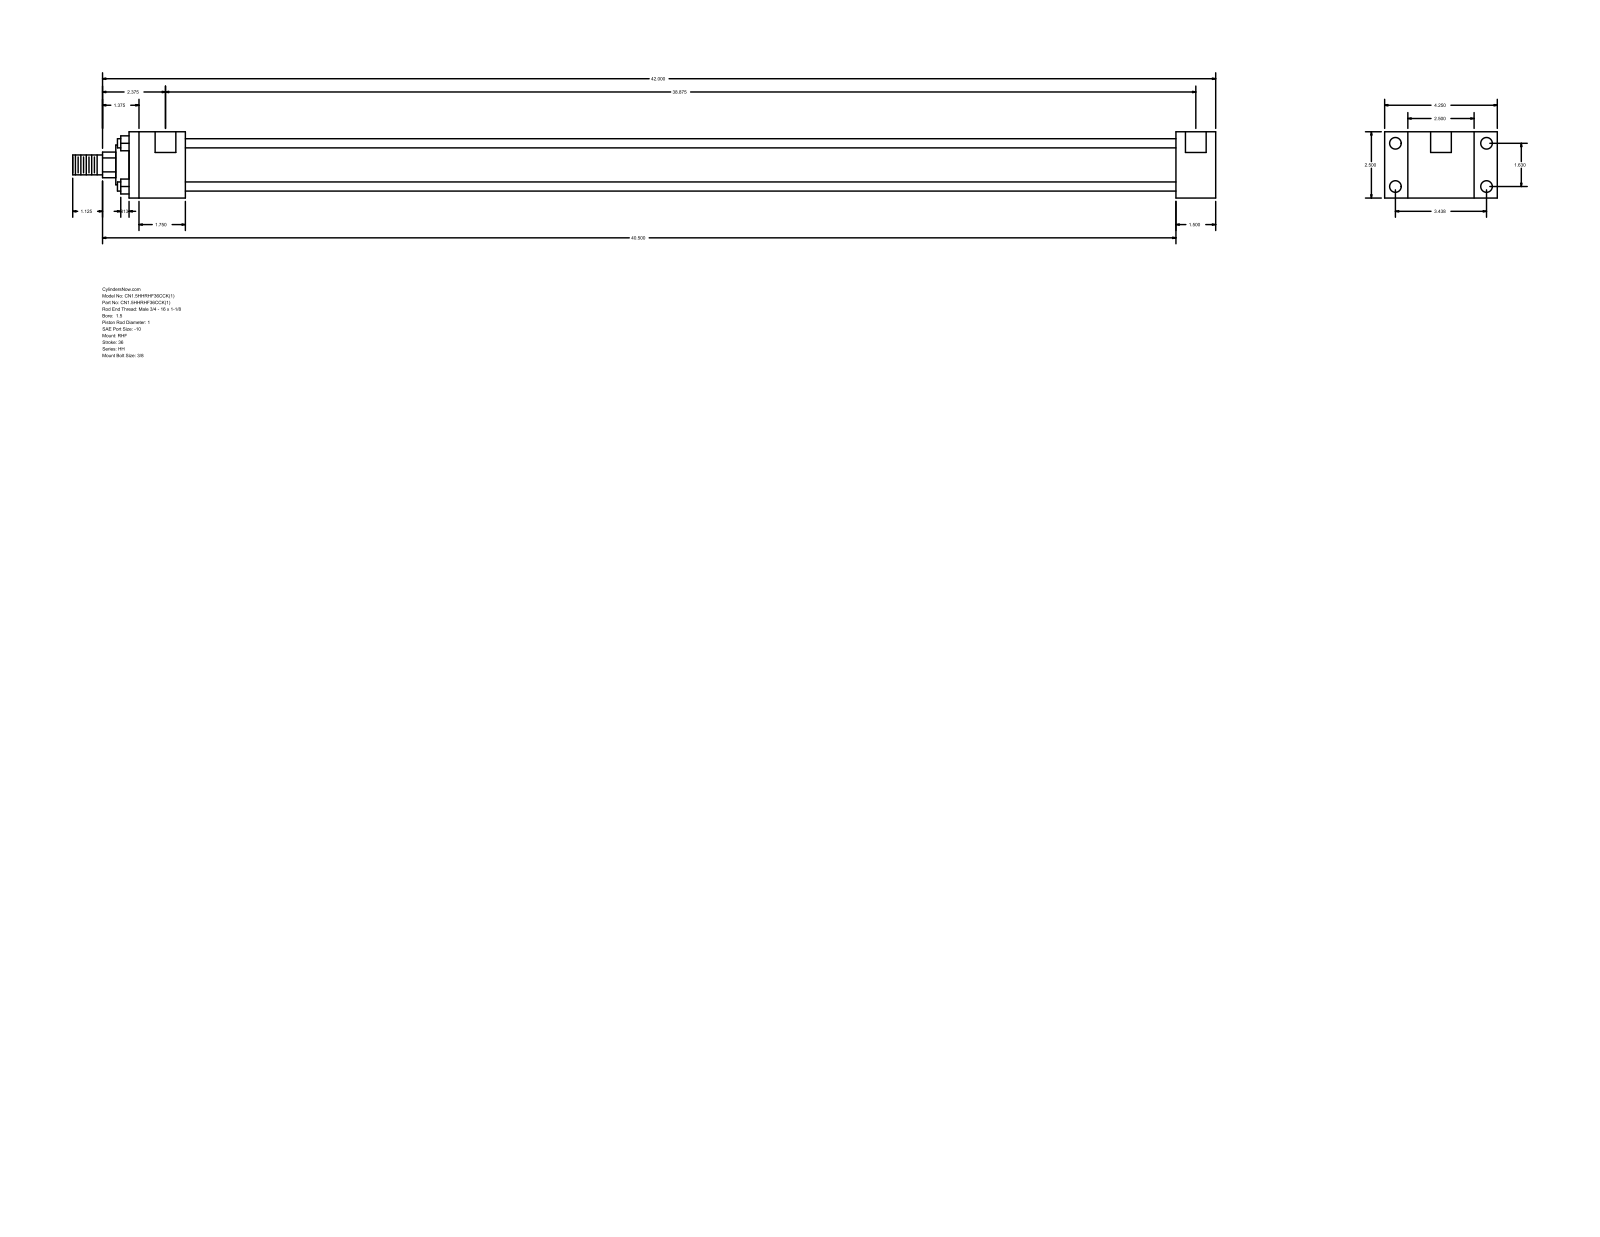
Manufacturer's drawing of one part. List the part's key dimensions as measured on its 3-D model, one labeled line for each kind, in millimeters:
Part name (STEP PRODUCT): HH_RHF__0150_1
STEP written by: GSSL Pune (CONFIG_CONTROL_DESIGN)
Units: millimetres
Bodies: 0 solids, 88 faces (60 planar, 28 cylindrical, 0 other)
Overall size (bounding box): 1095.38 × 107.95 × 63.5
Round holes (diameter × count): ⌀5.56 ×4, ⌀11.13 ×4, ⌀19.84 ×2
Round bosses / shafts (diameter × count): ⌀8.76 ×4, ⌀44.45 ×1, ⌀38.1 ×1, ⌀25.4 ×1, ⌀19.05 ×1
Partial cylindrical surfaces — rounded edges, fillets, slot ends (radius × count): R12.29 ×1
Main face-to-face distances: 63.5, 22.23, 85.73, 38.1, 107.96, 949.32, 987.42, 53.98, 1003.3, 1041.4
Hole centre spacings: 1.59, 41.4, 87.32, 96.64, 989.01, 990.6, 987.42
